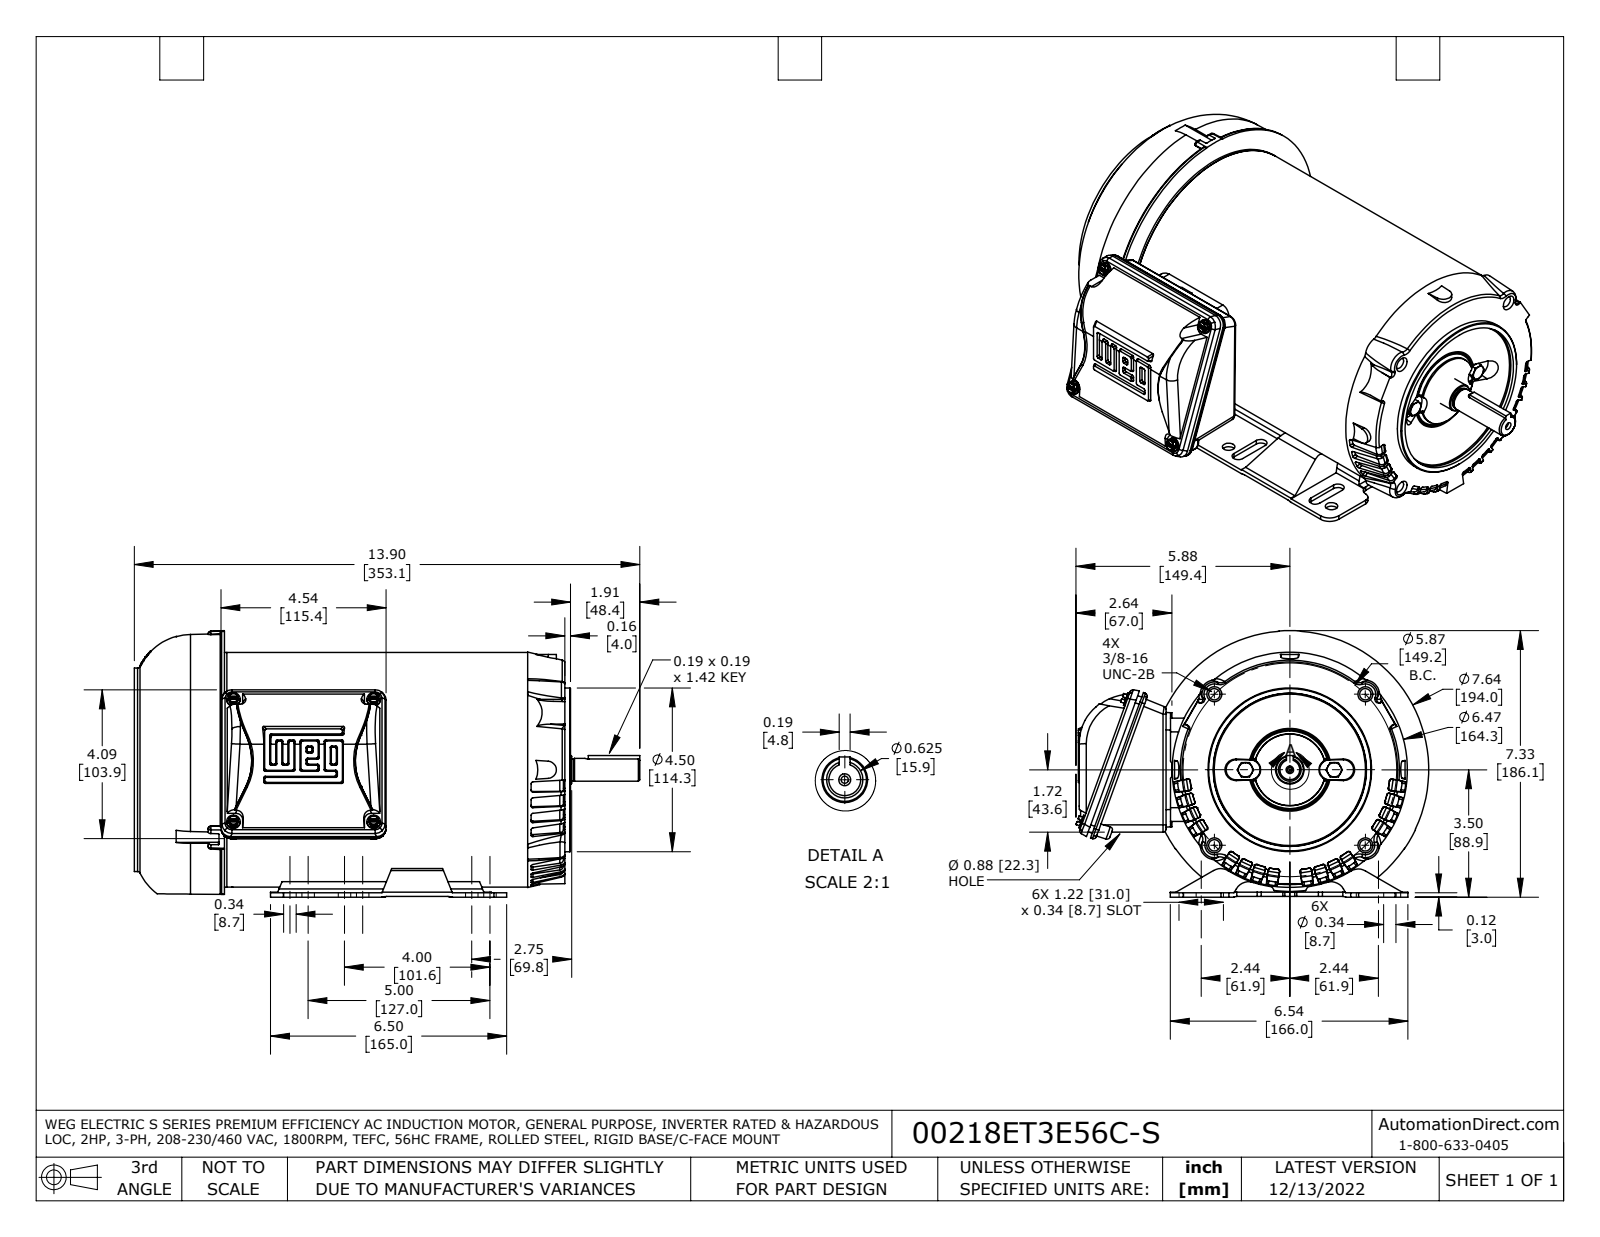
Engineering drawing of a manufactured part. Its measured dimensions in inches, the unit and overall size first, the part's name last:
Units: inches
Overall size (bounding box): 13.902 × 9.7 × 7.551
Round holes (diameter × count): ⌀0.343 ×6, ⌀0.313 ×4, ⌀0.124 ×1
Round bosses / shafts (diameter × count): ⌀0.374 ×4, ⌀0.35 ×2, ⌀6.447 ×1, ⌀6.447 ×1, ⌀5.591 ×1, ⌀4.5 ×1, ⌀0.783 ×1, ⌀0.625 ×1
Partial cylindrical surfaces — rounded edges, fillets, slot ends (radius × count): R0.047 ×40, R0.006 ×38, R0.051 ×32, R0.059 ×12, R0.087 ×12, R0.171 ×12, R0.02 ×10, R0.079 ×8
Main face-to-face distances: 8.268, 0.12, 0.067, 8.335, 2.283, 2.35, 10.618, 11.642, 9.358, 9.291
Hole centre spacings: 2.937, 4.154, 5.5, 1, 4, 5, 5.59, 5.874
Volume: 438.3 in³ · Surface area: 729.3 in²
Bodies: 14 solids, 1483 faces (557 planar, 355 cylindrical, 571 other)
Part name (STEP PRODUCT): 56HC_3PH_TEFC_GP_13898 broken base surfs w 1PHNB 1 fxt
STEP written by: SolidWorks 2021 (AUTOMOTIVE_DESIGN)
